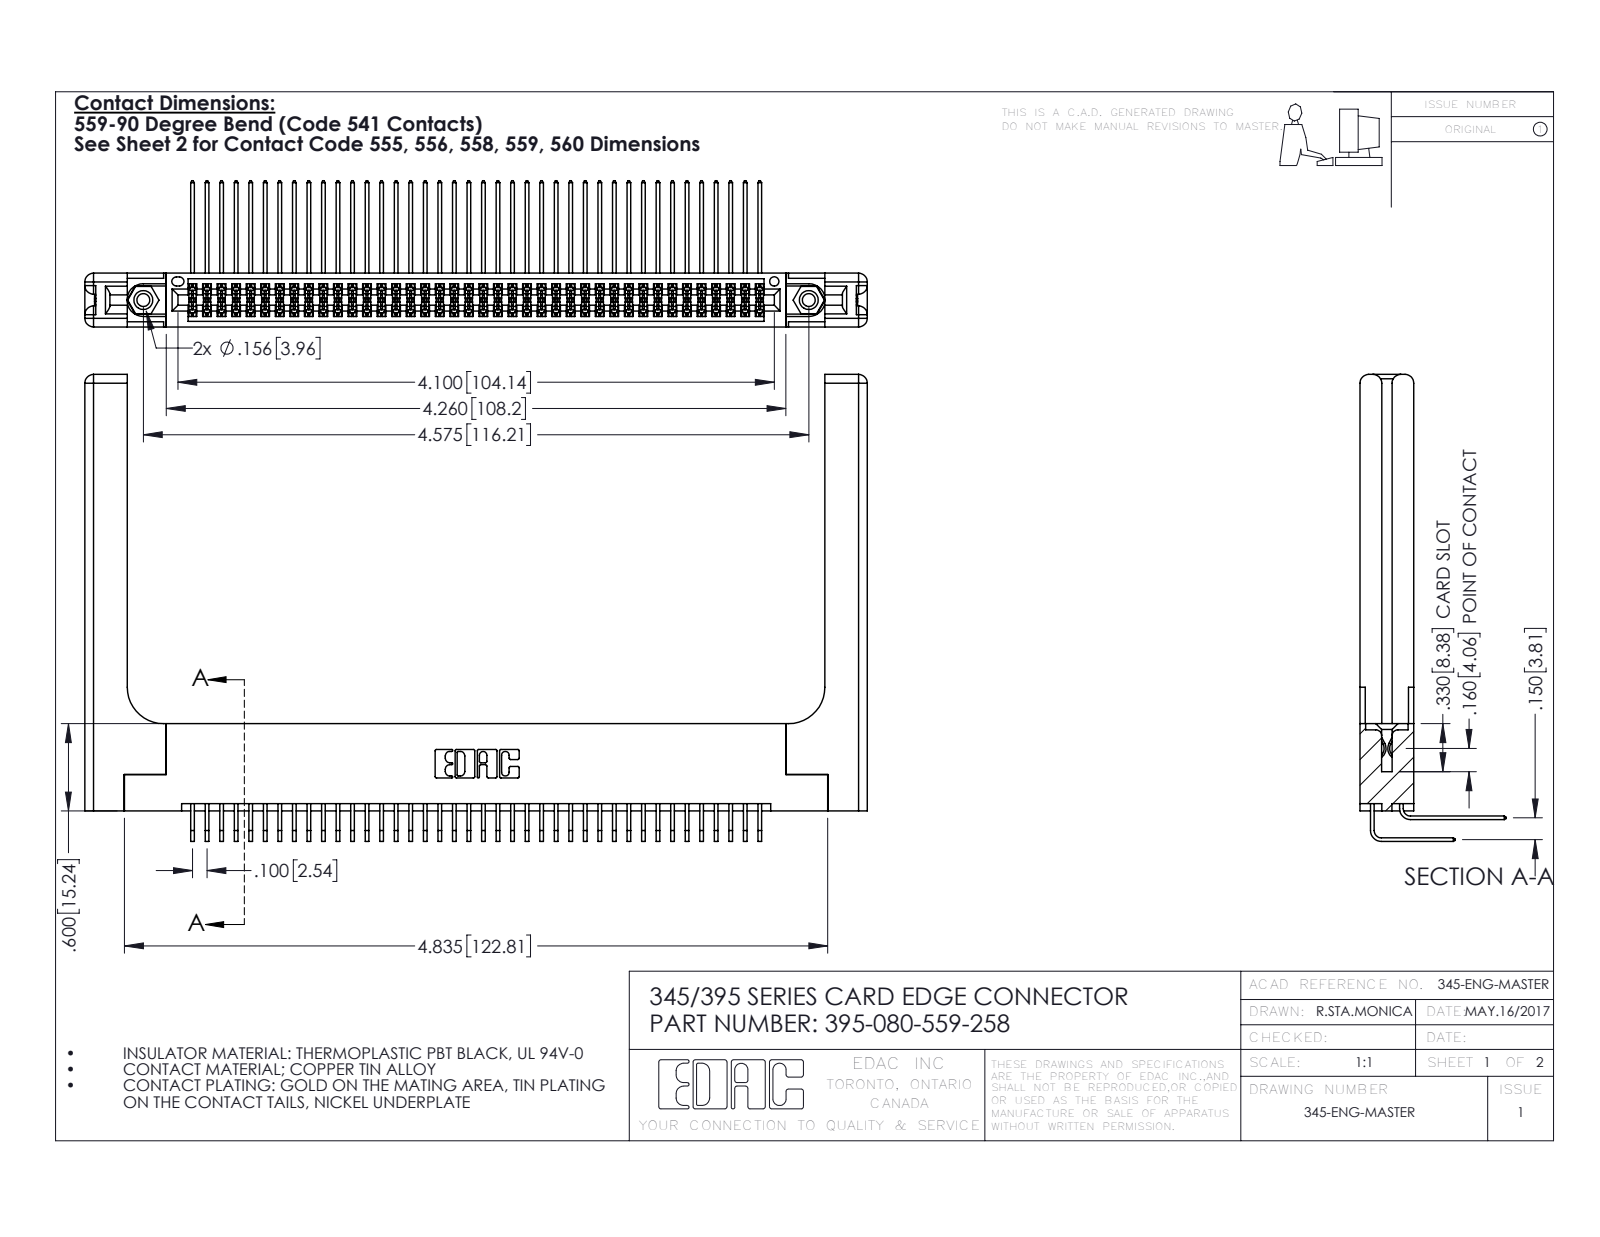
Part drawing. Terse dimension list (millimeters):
name: 345-250-001_345-250-001-102; 345-292-001_558 559 Tail - 1; 345-220-058_345-220-058; 395-080-559-258 (+2 more)
written by: SolidWorks 2016 (CONFIG_CONTROL_DESIGN)
unit: mm
bodies: 85 solids, 4542 faces (3028 planar, 1454 cylindrical, 60 other)
size: 136.6 × 81.5 × 25.5
volume: 22 190 mm³; area: 27 460 mm²
holes: 2× ⌀2.3, 2× ⌀3.2, 2× ⌀4, 1× ⌀1.6
bosses: 2× ⌀3.9
rounds: 121× R0.2, 22× R0.3, 16× R1.5, 6× R0.2, 6× R0.8, 3× R0.7, 2× R0.4, 2× R0.5
face distances: 1.8, 9.4, 7.6, 5.1, 2.5, 6.9, 0.6, 5.7, 4.4, 3.8
hole spacings: 6.9, 110.2, 116.2
